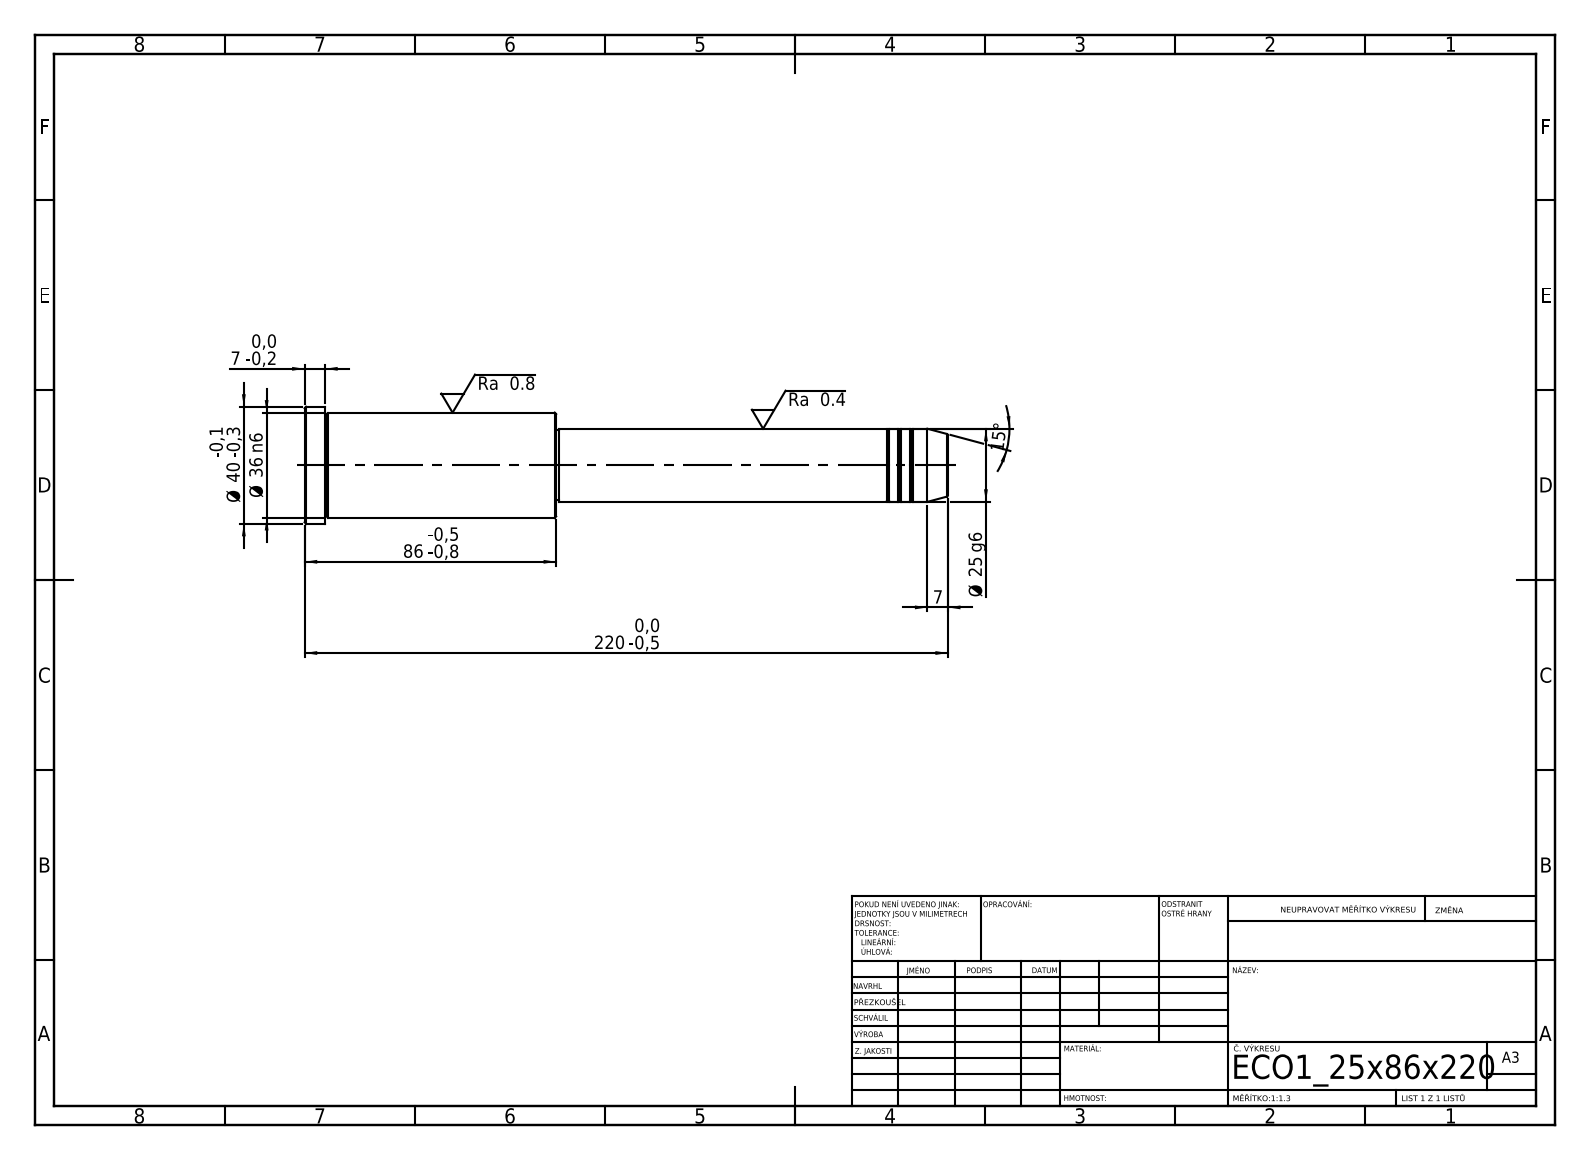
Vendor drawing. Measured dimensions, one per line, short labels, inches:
written by: SolidWorks 2019 (CONFIG_CONTROL_DESIGN)
unit: in
bodies: 1 solid, 43 faces (5 planar, 14 cylindrical, 24 other)
size: 8.661 × 1.575 × 1.575
volume: 9.415 in³; area: 35.45 in²
bosses: 1× ⌀1.575, 1× ⌀1.417, 1× ⌀0.984, 1× ⌀0.945
face distances: 3.386, 5.276, 8.661, 8.386, 3.11, 0.276, 5.236, 0.039, 3.15, 3.425
